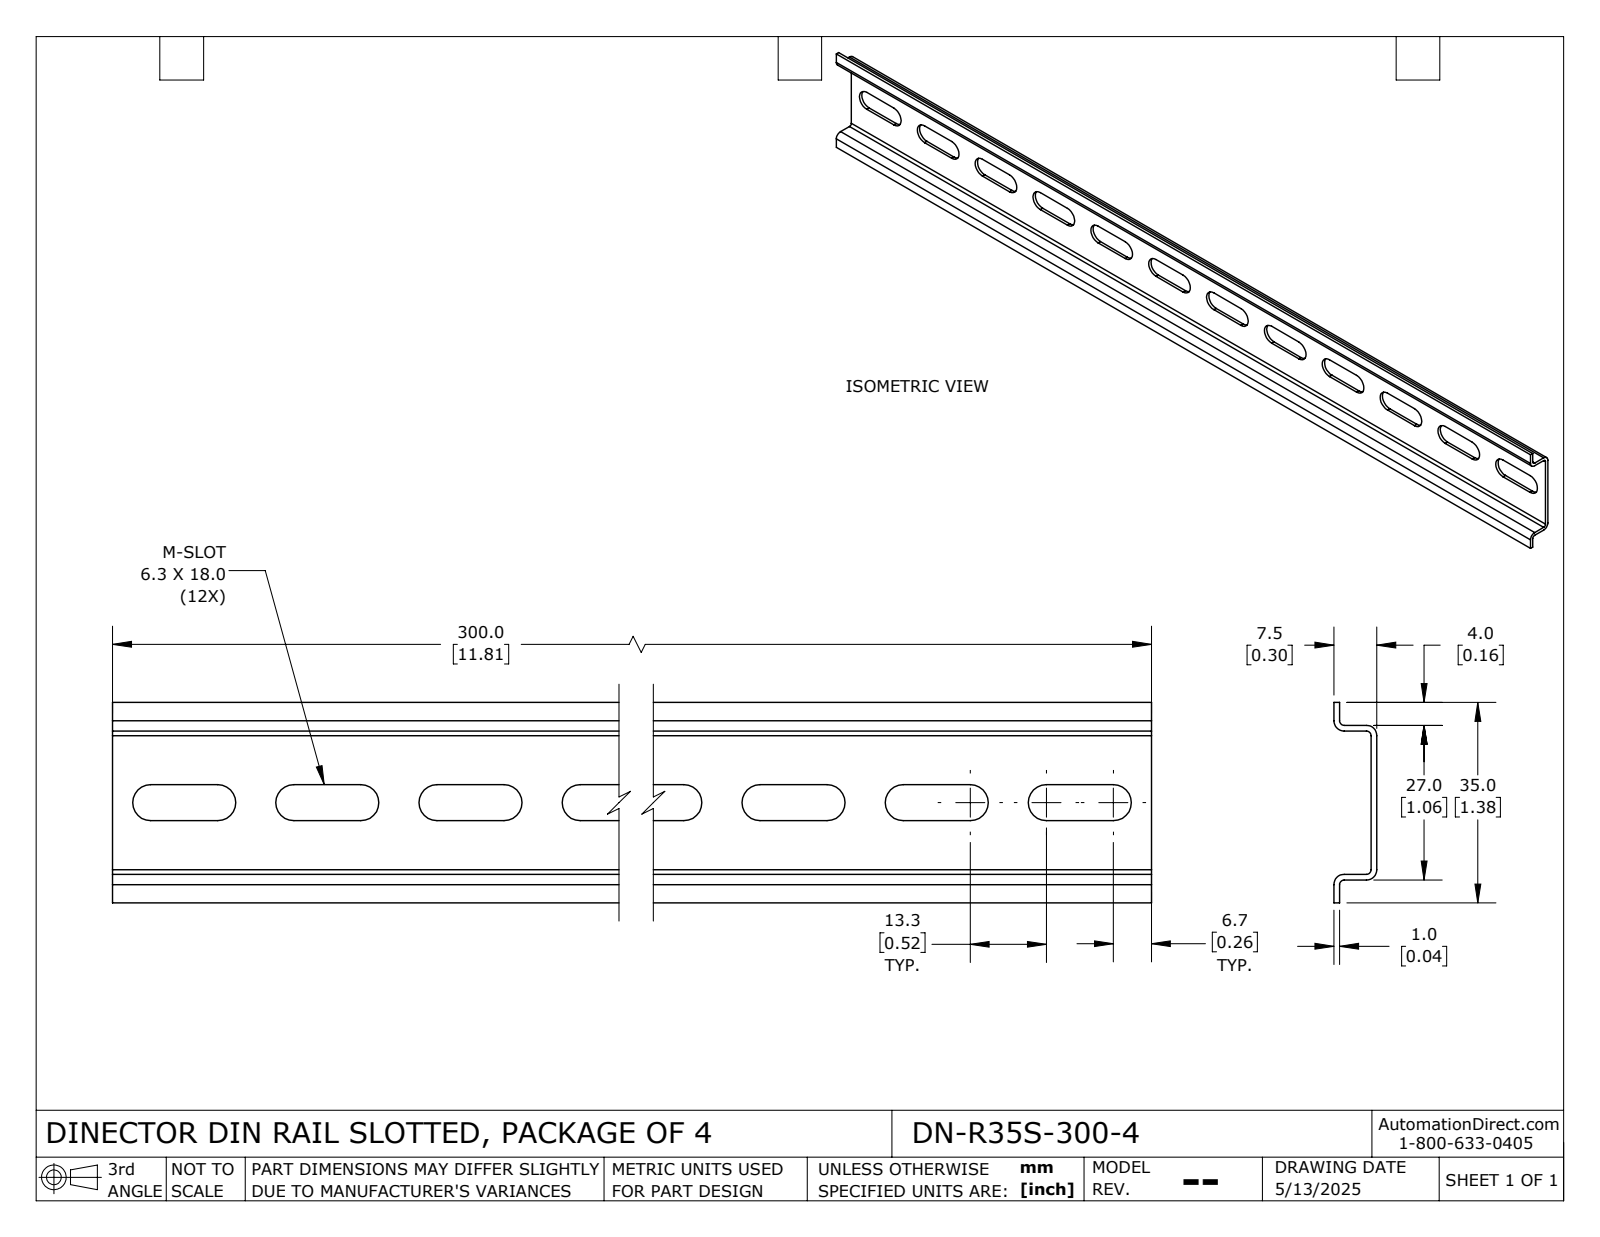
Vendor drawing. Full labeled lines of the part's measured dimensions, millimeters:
Part name (STEP PRODUCT): DN-R35S-300-4_Default
STEP written by: SolidWorks 2024 (CONFIG_CONTROL_DESIGN)
Units: millimetres
Bodies: 1 solid, 70 faces (38 planar, 32 cylindrical, 0 other)
Overall size (bounding box): 300 × 35 × 7.5
Volume: 12 472 mm³ · Surface area: 26 154 mm²
Partial cylindrical surfaces — rounded edges, fillets, slot ends (radius × count): R3.15 ×24, R0.8 ×4, R1.8 ×4
Main face-to-face distances: 1, 6.5, 26, 7.5, 5.5, 27, 25, 4, 5, 30
